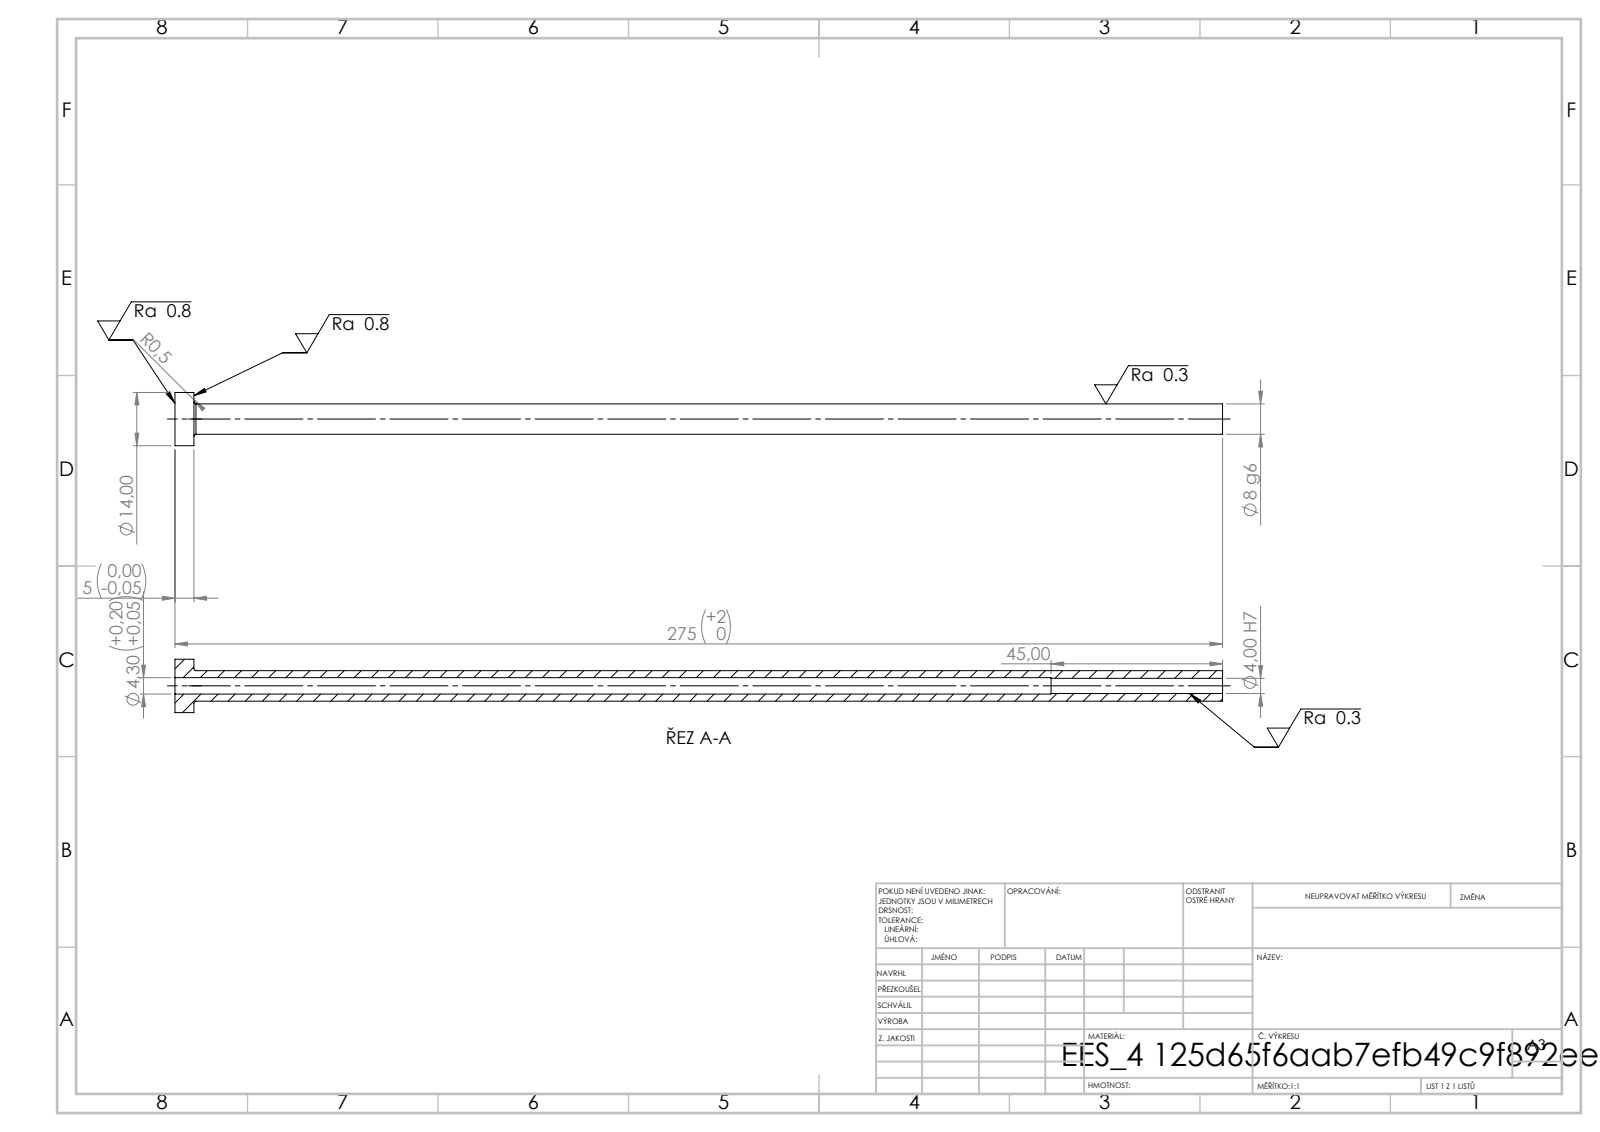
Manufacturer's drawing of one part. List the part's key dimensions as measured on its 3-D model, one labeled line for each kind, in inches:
STEP written by: SolidWorks 2019 (CONFIG_CONTROL_DESIGN)
Units: inches
Bodies: 1 solid, 14 faces (4 planar, 8 cylindrical, 2 other)
Overall size (bounding box): 10.827 × 0.551 × 0.551
Volume: 0.637 in³ · Surface area: 16.98 in²
Round holes (diameter × count): ⌀0.157 ×1, ⌀0.169 ×1
Round bosses / shafts (diameter × count): ⌀0.551 ×1, ⌀0.315 ×1
Main face-to-face distances: 0.197, 10.827, 10.63, 9.055, 8.858, 1.772
